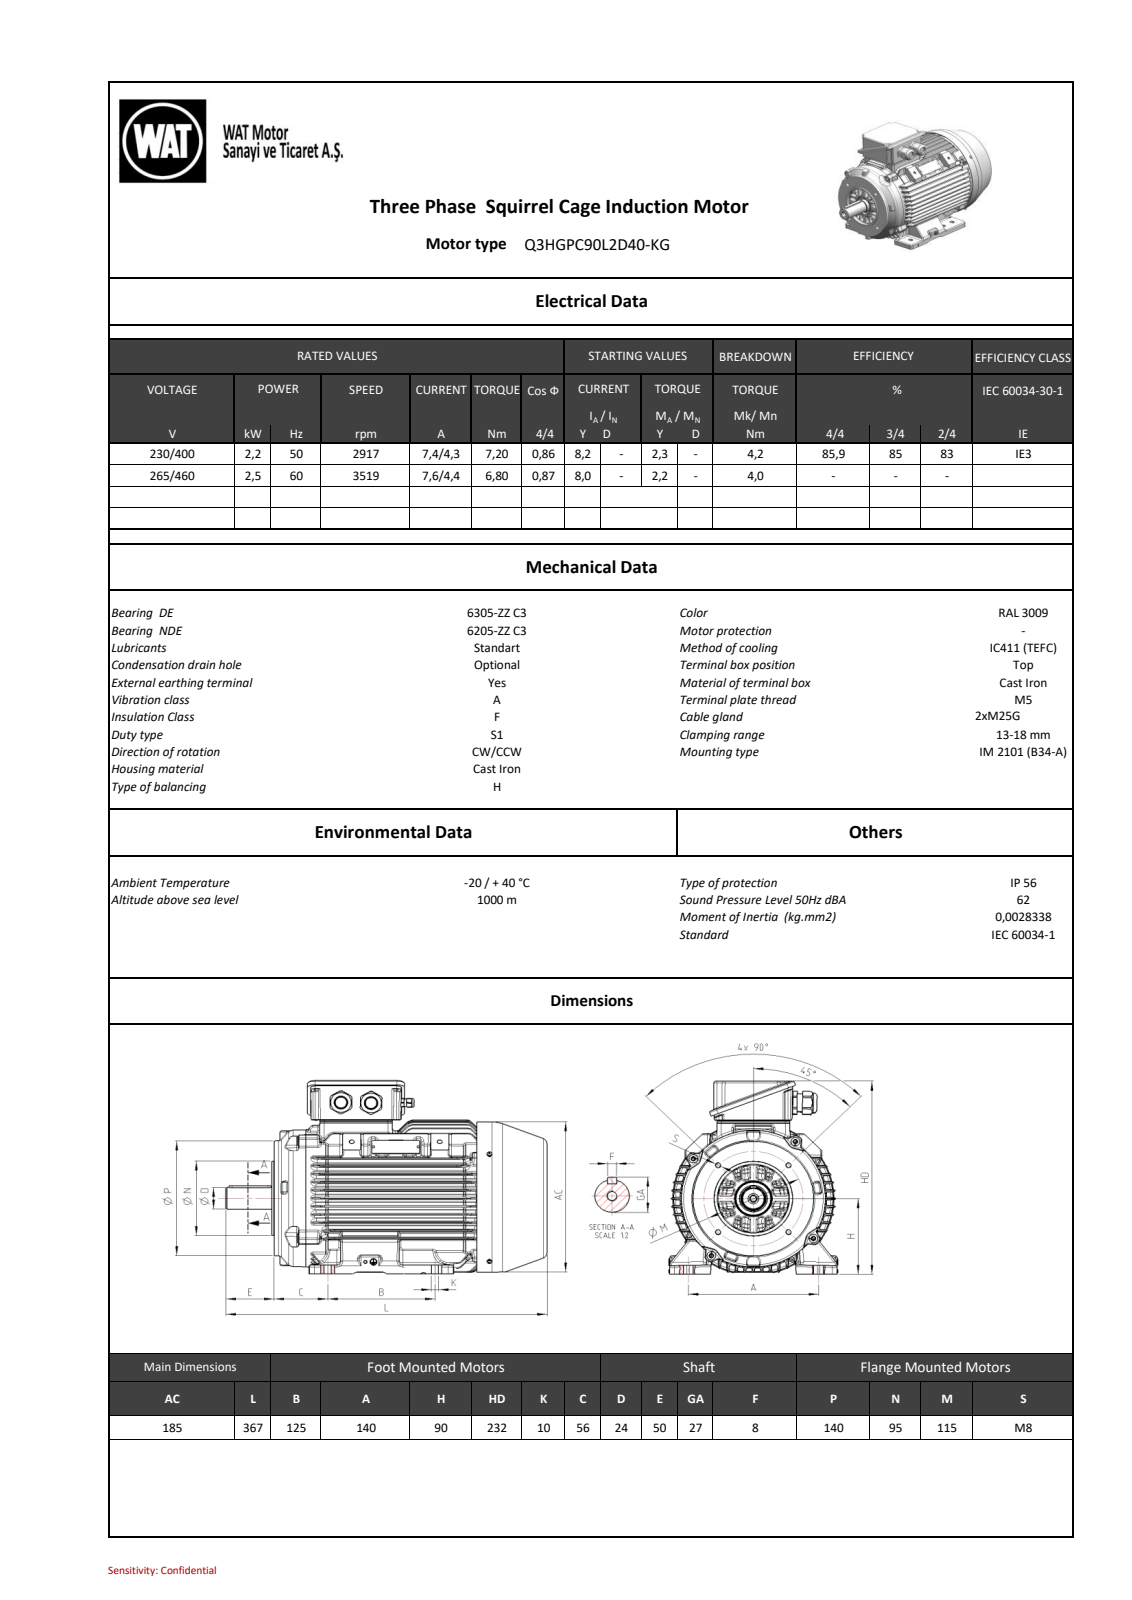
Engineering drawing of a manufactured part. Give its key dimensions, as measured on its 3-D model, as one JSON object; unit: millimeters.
{"part_name": "26000A30F4D8roqg", "step_written_by": "SIEMENS PLM Software NX 11.0 (AUTOMOTIVE_DESIGN)", "units": "millimeters", "bodies": {"solids": 0, "faces": 2942, "planar": 837, "cylindrical": 844, "other": 1261}, "overall_size": [368.42, 231.98, 226.53], "round_holes": [[6.8, 5], [4.2, 3], [10, 3], [2.5, 2], [17.2, 2], [6.5, 1], [8.4, 1], [36.9, 1], [37.1, 1], [174, 1]], "round_bosses_or_shafts": [[20, 4], [8.65, 3], [8.5, 3], [8, 3], [5, 3], [27.7, 2], [25.25, 2], [9.2, 2]], "partial_cylinders_radius": [[1.5, 257], [1, 42], [4, 38], [2, 37], [5, 24], [1.8, 20], [3, 16], [26.5, 12]], "face_to_face_distances": [12.04, 268.63, 3, 49.79, 318.42, 62.58, 3.01, 1.5, 12.05, 1.53], "hole_center_spacings": [81.31, 57.49, 114.99, 40, 57.5, 70.71, 75.01, 95.22]}
